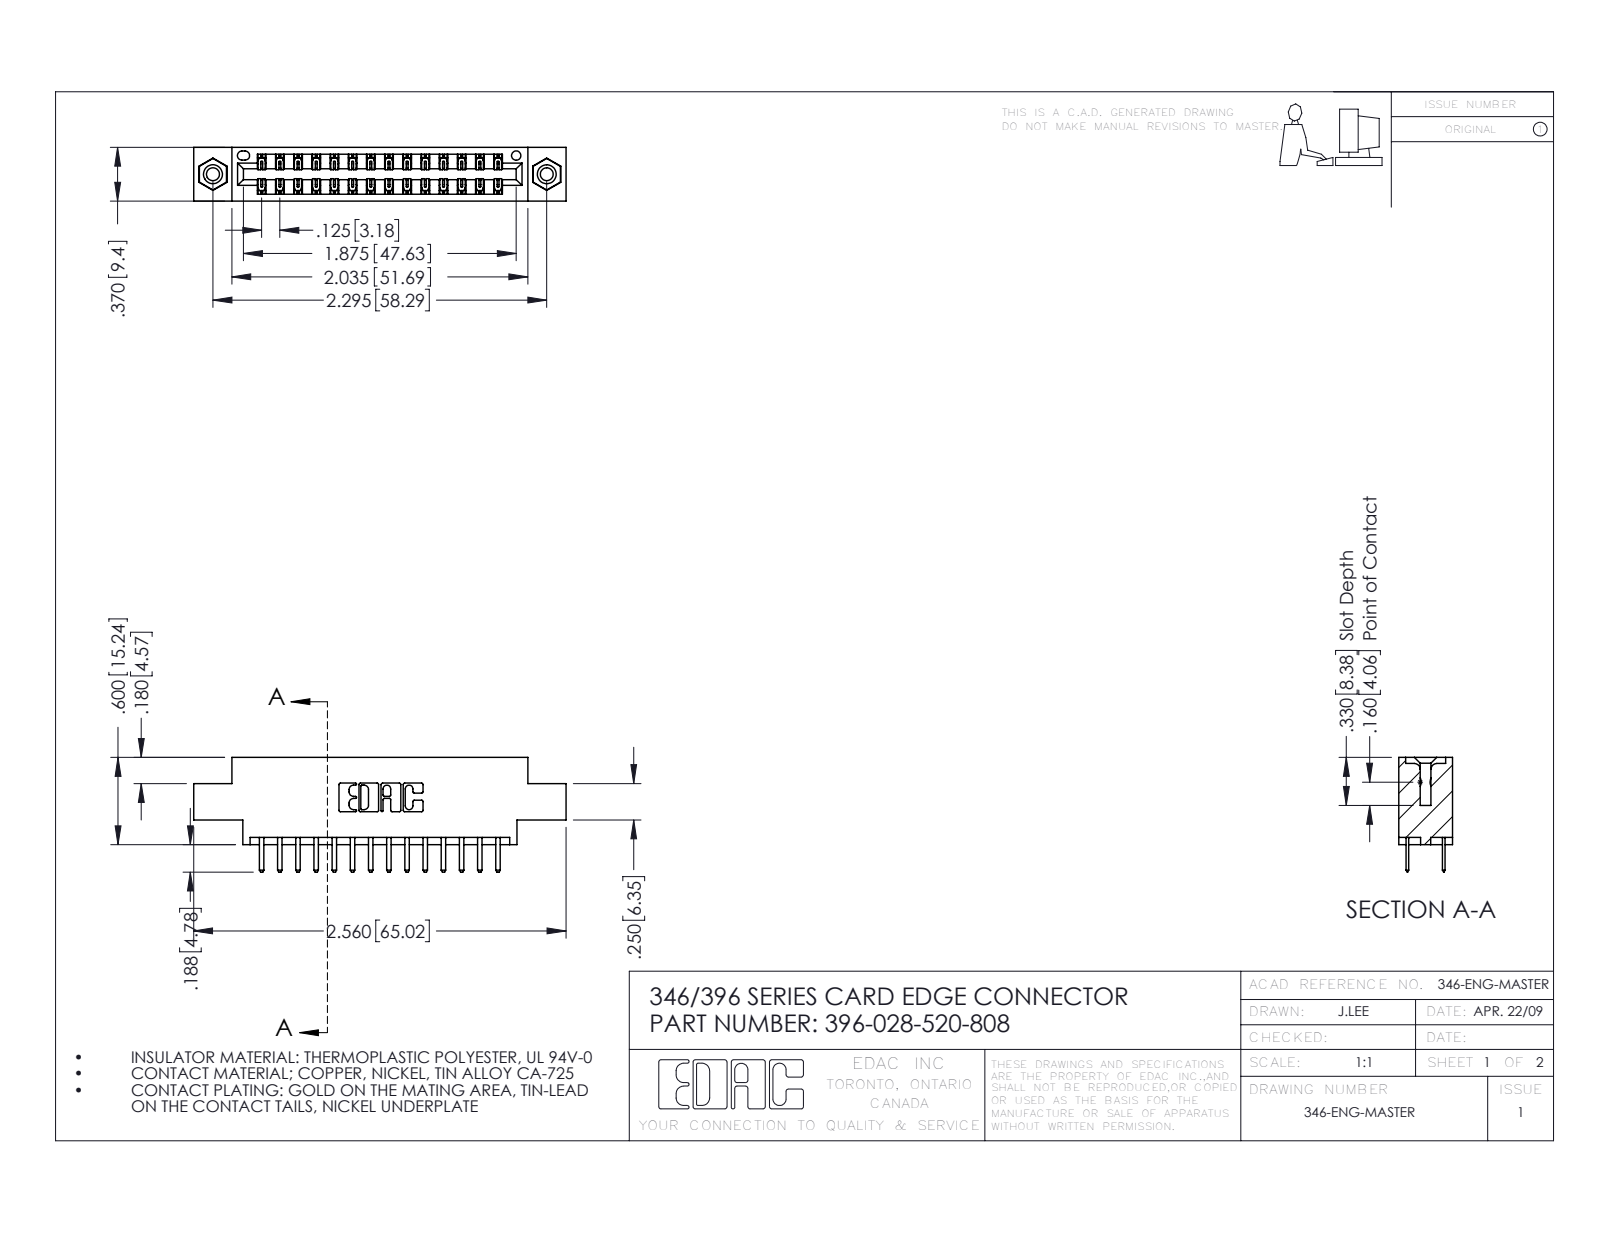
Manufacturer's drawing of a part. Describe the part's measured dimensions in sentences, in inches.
The part is named "345-250-001_345-250-003-102; 345-292-001_345-293-120; 346 Part_0.170 Offset - 0.156 Dia-TI; 396-028-520-808". Its 3-D file was written by "SolidWorks 2016 (CONFIG_CONTROL_DESIGN)". It is 31 solids with 1754 faces: 1148 planar, 590 cylindrical and 16 other. Overall it measures 2.56 by 0.788 by 0.37 inches. Its volume is 0.363 cubic inches and its surface area 12.26 square inches. Round holes: 2 of diameter 0.089, 2 of diameter 0.125, 2 of diameter 0.156, 1 of diameter 0.064. Round bosses or shafts: 2 of diameter 0.155. Partial cylindrical surfaces (rounded edges, fillets, slot ends): 42 of radius 0.006, 32 of radius 0.01, 22 of radius 0.01, 6 of radius 0.007, 6 of radius 0.031, 3 of radius 0.026, 2 of radius 0.014, 2 of radius 0.022. The main face-to-face distances are 0.25, 0.048, 0.322, 0.37, 0.222, 0.148, 0.275, 0.072, 0.298, 0.025. The hole center spacings are 0.246, 2.089, 2.295.
